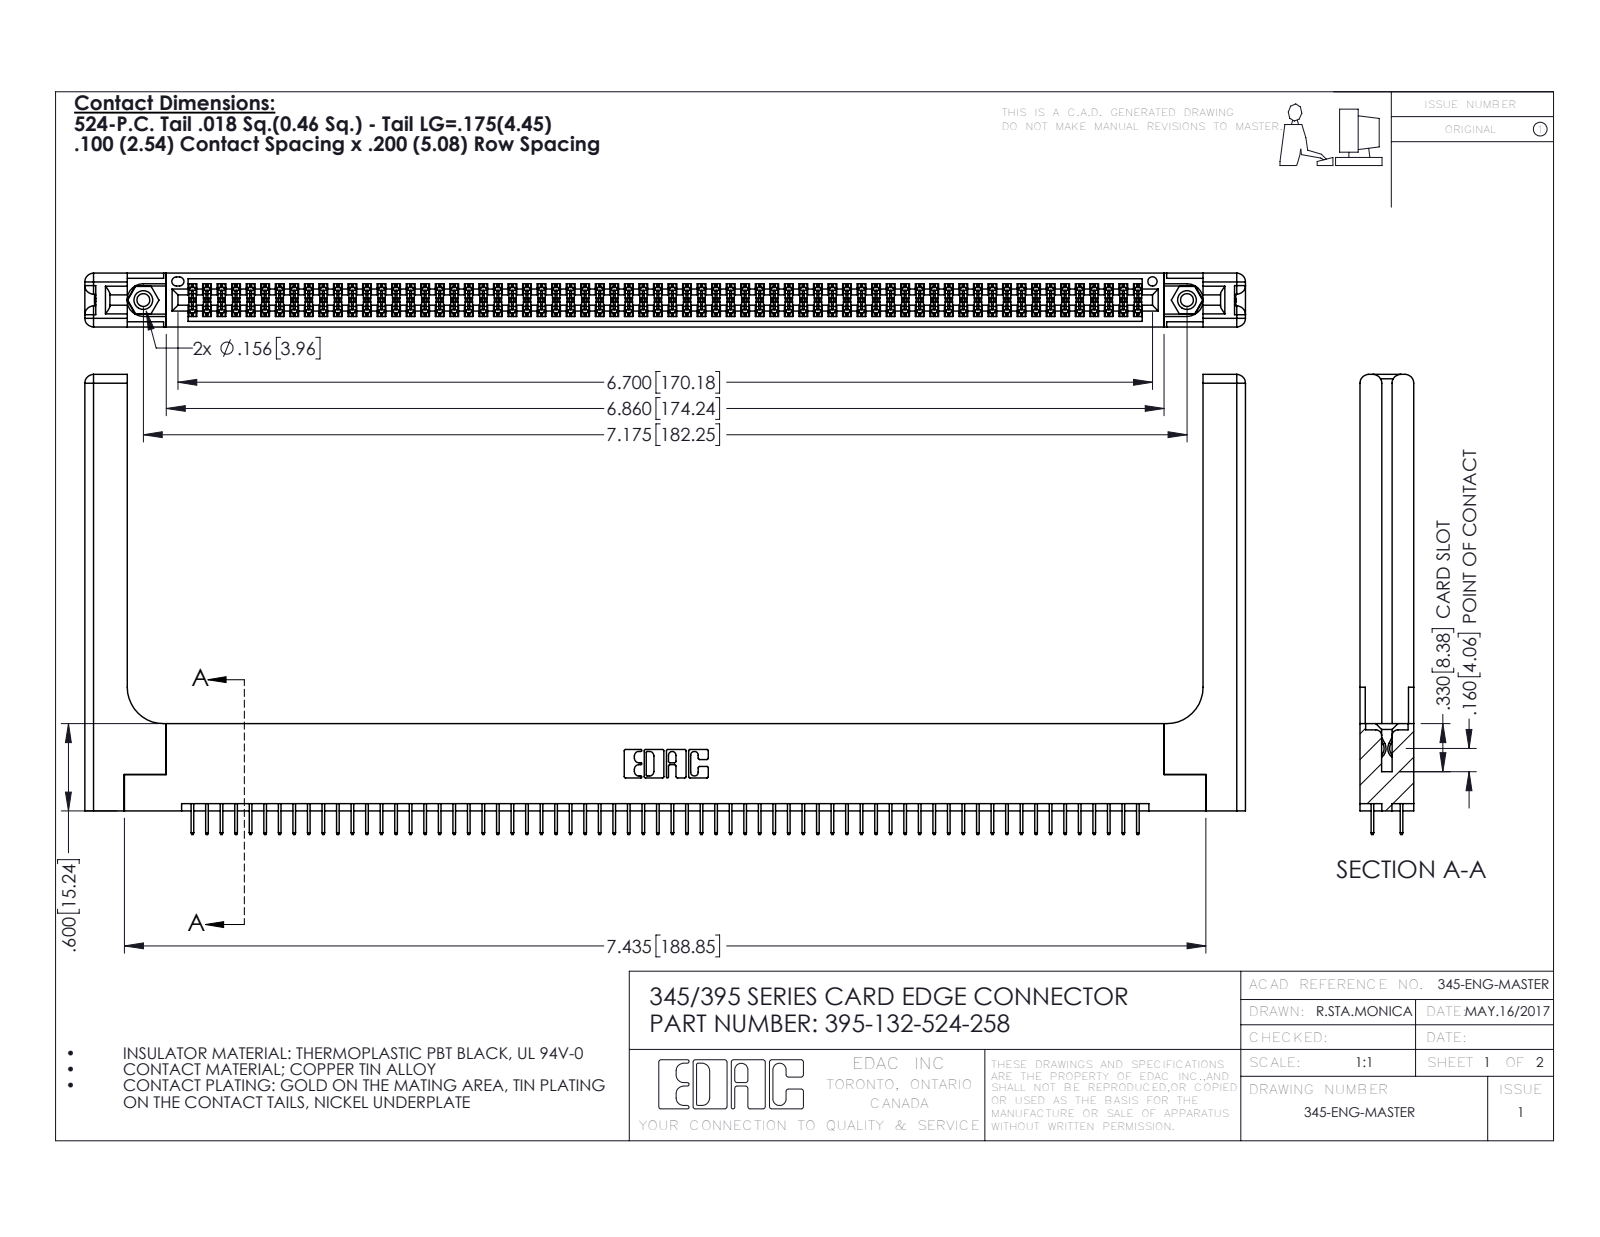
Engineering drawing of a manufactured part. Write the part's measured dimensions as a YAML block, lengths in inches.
part_name: "345-292-001_345-293-124; 395-132-524-258; 345 Part_Flush Mounting Lugs - 0.156 Dia-TH; 345-250-001_345-250-001-102 (+1 more)"
step_written_by: "SolidWorks 2016 (CONFIG_CONTROL_DESIGN)"
units: inches
bodies: {solids: 137, faces: 7510, planar: 5376, cylindrical: 2074, other: 60}
overall_size: [7.979, 3.162, 0.37]
volume: 1.72
surface_area: 52.9
round_holes:
  - {diameter: 0.089, count: 2}
  - {diameter: 0.125, count: 2}
  - {diameter: 0.156, count: 2}
  - {diameter: 0.064, count: 1}
round_bosses_or_shafts:
  - {diameter: 0.155, count: 2}
partial_cylinders:
  - {radius: 0.006, count: 198}
  - {radius: 0.01, count: 22}
  - {radius: 0.06, count: 16}
  - {radius: 0.007, count: 6}
  - {radius: 0.031, count: 6}
  - {radius: 0.026, count: 3}
  - {radius: 0.014, count: 2}
  - {radius: 0.019, count: 2}
face_to_face_distances: [0.072, 0.298, 0.37, 0.2, 0.098, 0.272, 0.025, 0.225, 0.072, 0.148]
hole_center_spacings: [0.27, 6.939, 7.175]
